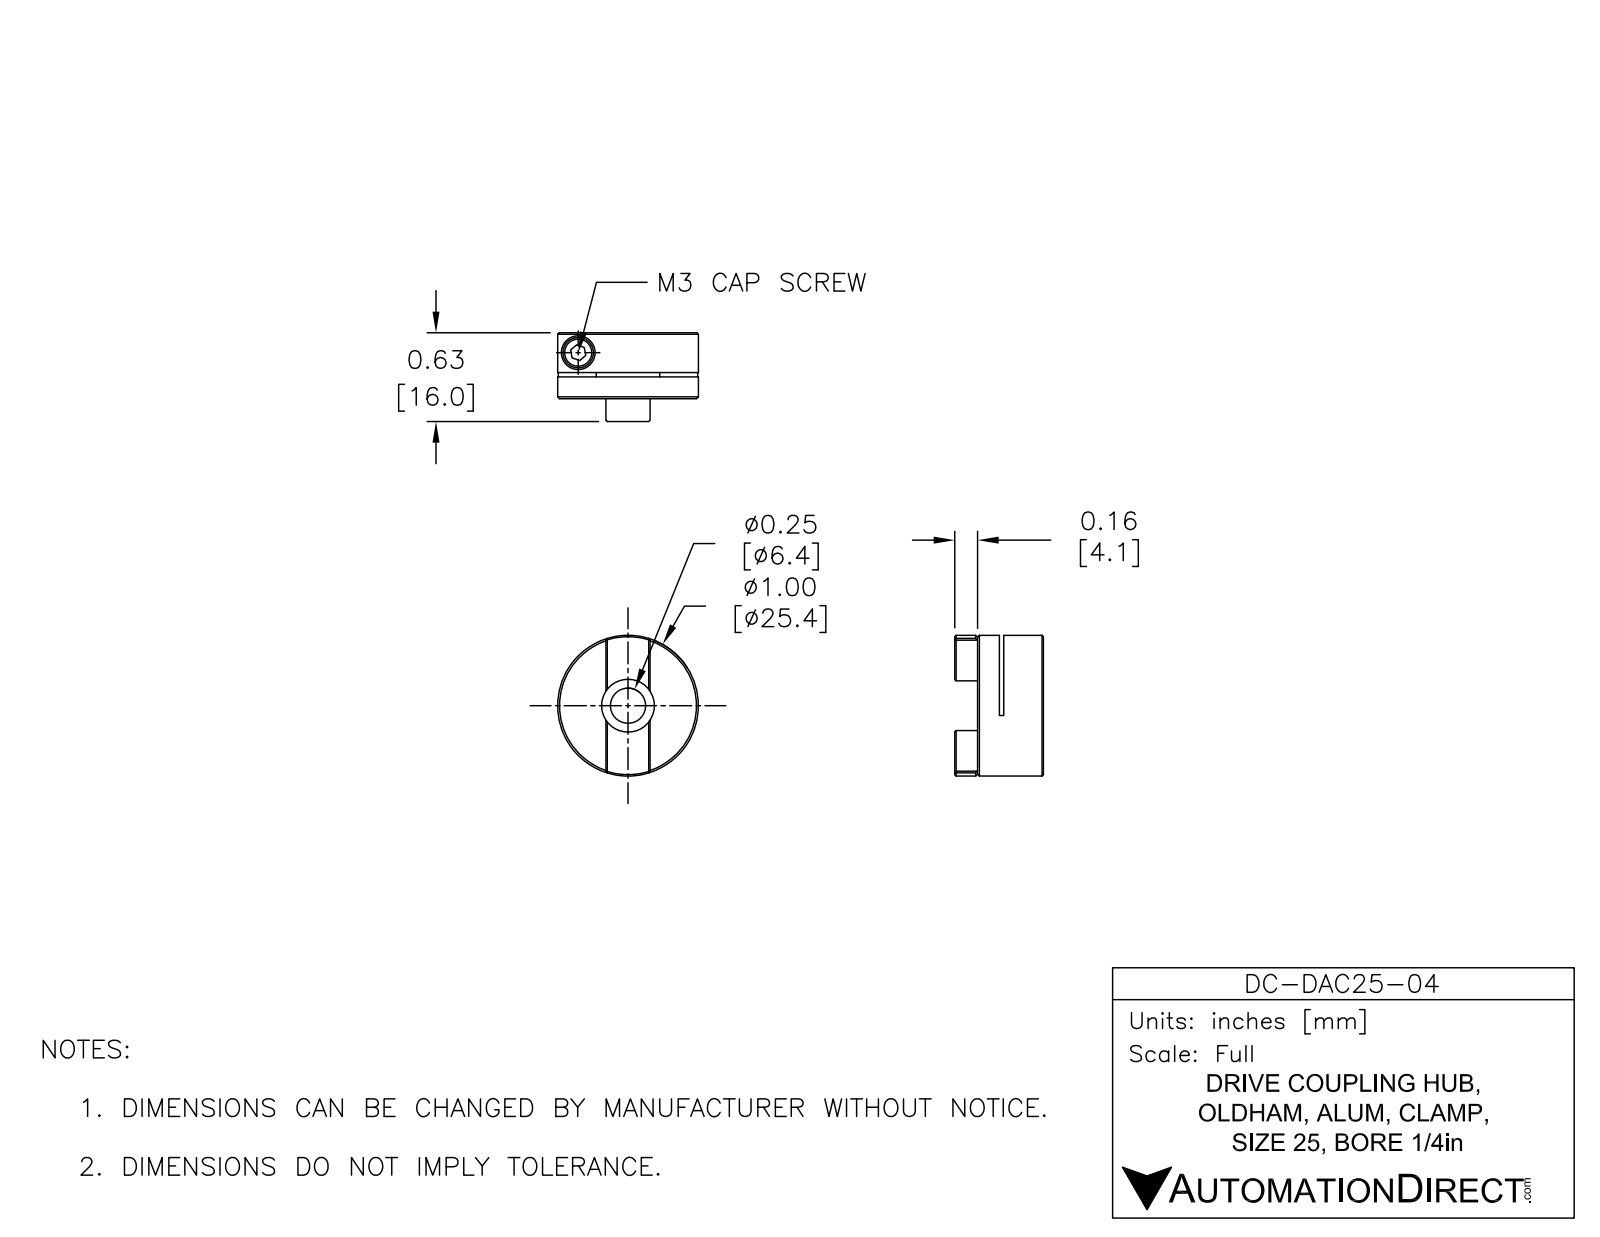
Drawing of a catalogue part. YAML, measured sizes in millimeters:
part_name: "DC-DAC25-04"
step_written_by: "SolidWorks 2015 (AUTOMOTIVE_DESIGN)"
units: millimeters
bodies: {solids: 1, faces: 55, planar: 29, cylindrical: 16, other: 10}
overall_size: [25.4, 25.4, 16]
volume: 5549
surface_area: 3265
round_holes:
  - {diameter: 2.46, count: 1}
  - {diameter: 3.4, count: 1}
  - {diameter: 6.1, count: 1}
  - {diameter: 6.35, count: 1}
  - {diameter: 9.53, count: 1}
round_bosses_or_shafts:
  - {diameter: 25.4, count: 1}
face_to_face_distances: [11.89, 7.95, 3.94, 7.16, 0.79, 4.73, 16, 8.84, 8.05, 4.11]
